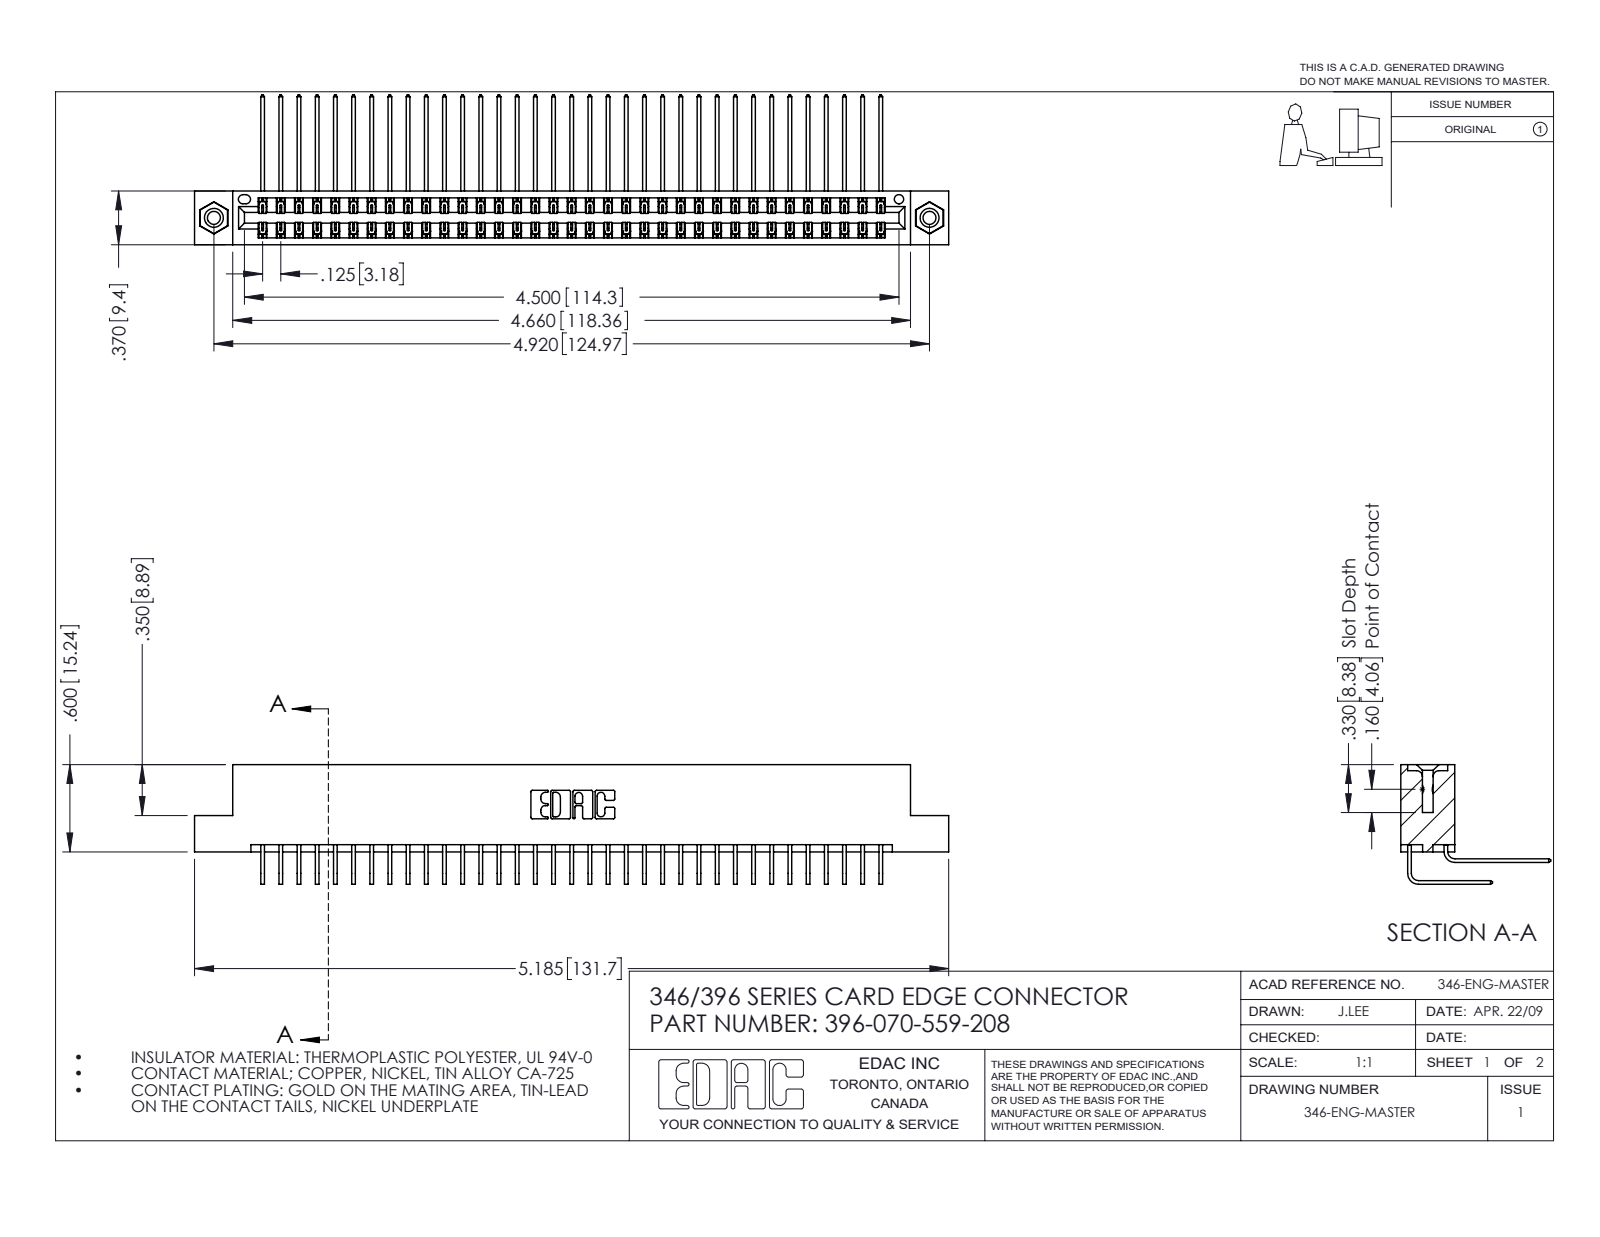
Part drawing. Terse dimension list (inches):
name: 346 Part_Flush Mounting Lugs - 0.156 Dia-TI; 396-070-559-208; 345-292-001_558 559 Tail - 1; 345-250-001_345-250-003-102 (+1 more)
written by: SolidWorks 2016 (CONFIG_CONTROL_DESIGN)
unit: in
bodies: 73 solids, 3962 faces (2698 planar, 1248 cylindrical, 16 other)
size: 5.185 × 1.03 × 0.823
volume: 0.805 in³; area: 30.96 in²
holes: 2× ⌀0.089, 2× ⌀0.125, 2× ⌀0.156, 1× ⌀0.064
bosses: 2× ⌀0.155
rounds: 105× R0.006, 22× R0.01, 6× R0.007, 6× R0.031, 3× R0.026, 2× R0.014, 2× R0.022, 2× R0.024
face distances: 0.048, 0.322, 0.025, 0.37, 0.25, 0.072, 0.298, 0.275, 0.148, 0.222
hole spacings: 0.246, 4.711, 4.92
